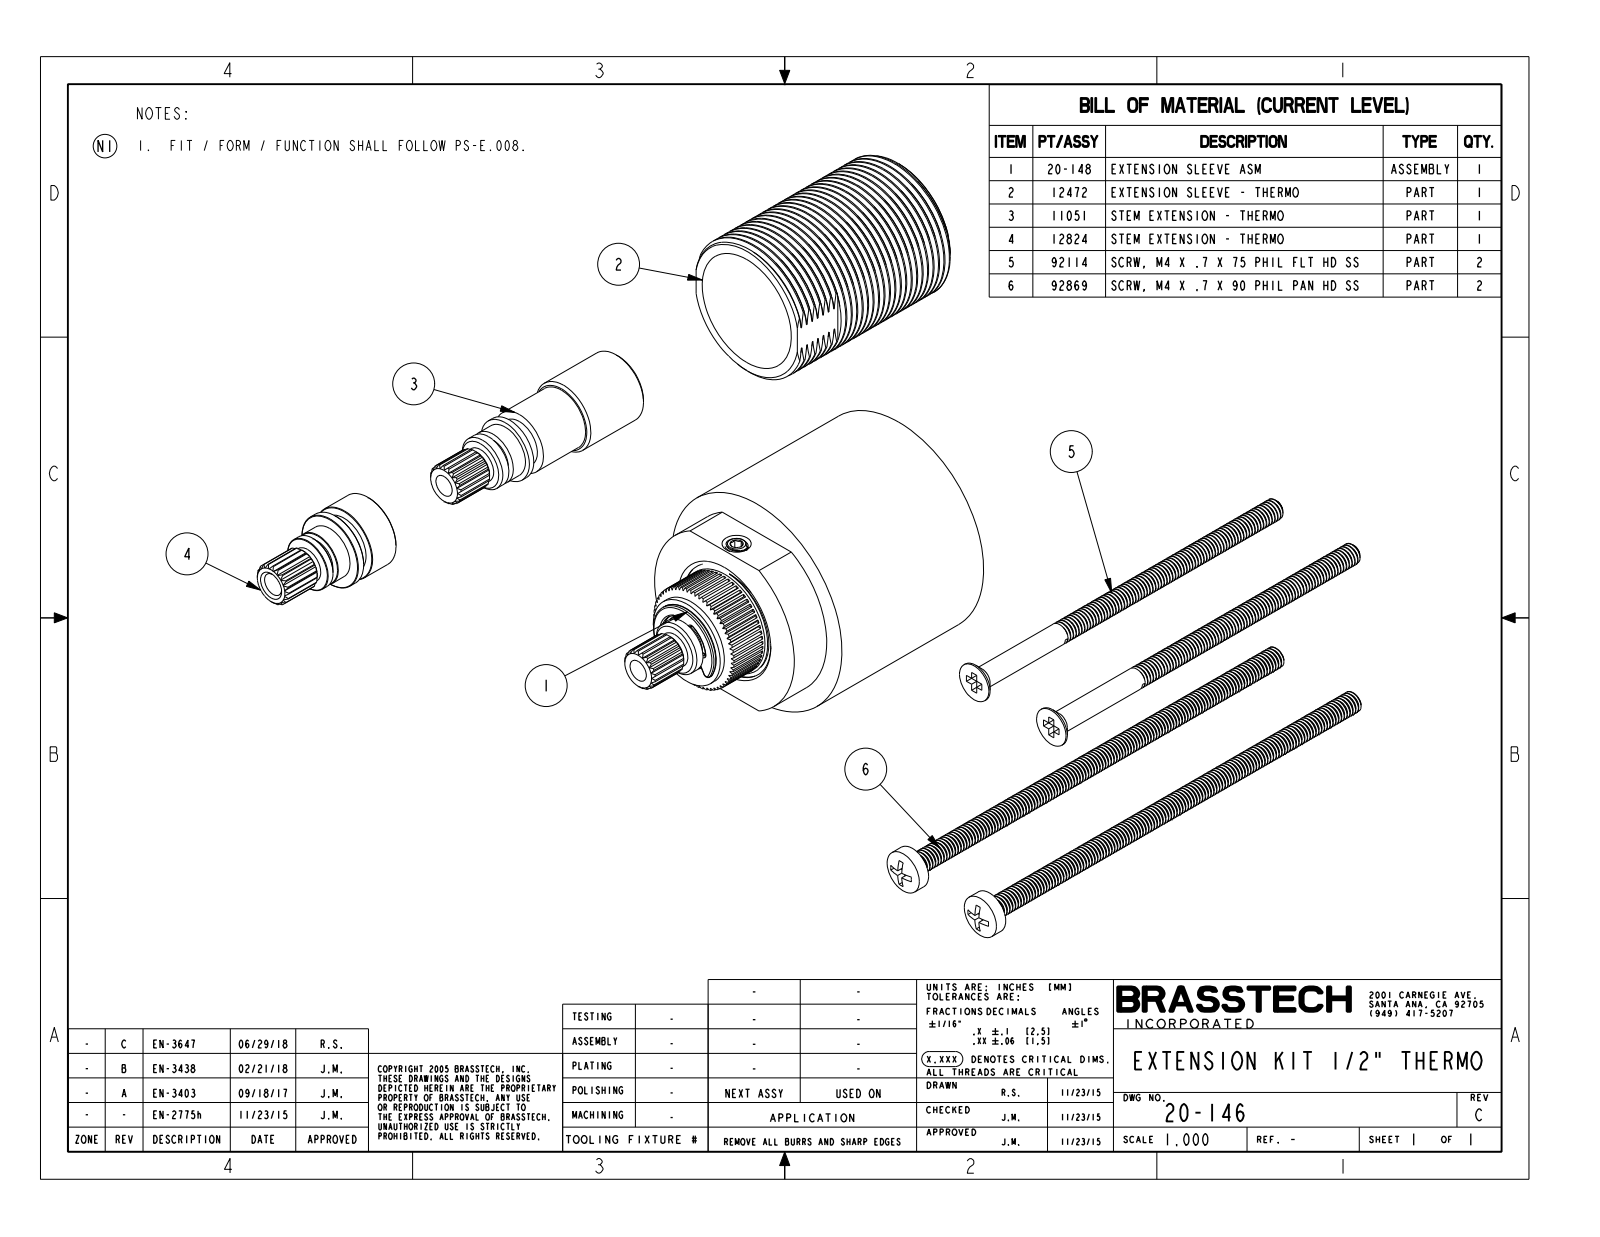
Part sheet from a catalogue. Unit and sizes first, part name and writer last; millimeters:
Units: millimetres
Overall size (bounding box): 204.3 × 150.6 × 88.1
Round holes (diameter × count): ⌀10.2 ×1, ⌀12.7 ×1, ⌀22 ×1, ⌀22.8 ×1, ⌀24.5 ×1, ⌀27 ×1, ⌀34.7 ×1, ⌀38 ×1
Round bosses / shafts (diameter × count): ⌀13.5 ×2, ⌀11.9 ×2, ⌀10 ×2, ⌀8.9 ×2, ⌀8 ×2, ⌀7.5 ×2, ⌀7.2 ×2, ⌀6.5 ×2
Partial cylindrical surfaces — rounded edges, fillets, slot ends (radius × count): R0.3 ×12, R0.6 ×12, R3.8 ×2, R3.9 ×1, R5.5 ×1, R7.4 ×1, R17.2 ×1
Main face-to-face distances: 17.5, 9.4, 8, 25.5, 14, 35, 43, 26.9, 8, 22
Hole centre spacings: 63.5
Volume: 50 750 mm³ · Surface area: 33 370 mm²
Bodies: 8 solids, 2011 faces (437 planar, 1042 cylindrical, 532 other)
Part name (STEP PRODUCT): 20-146
STEP written by: CREO PARAMETRIC BY PTC INC, 2023134 (CONFIG_CONTROL_DESIGN)
